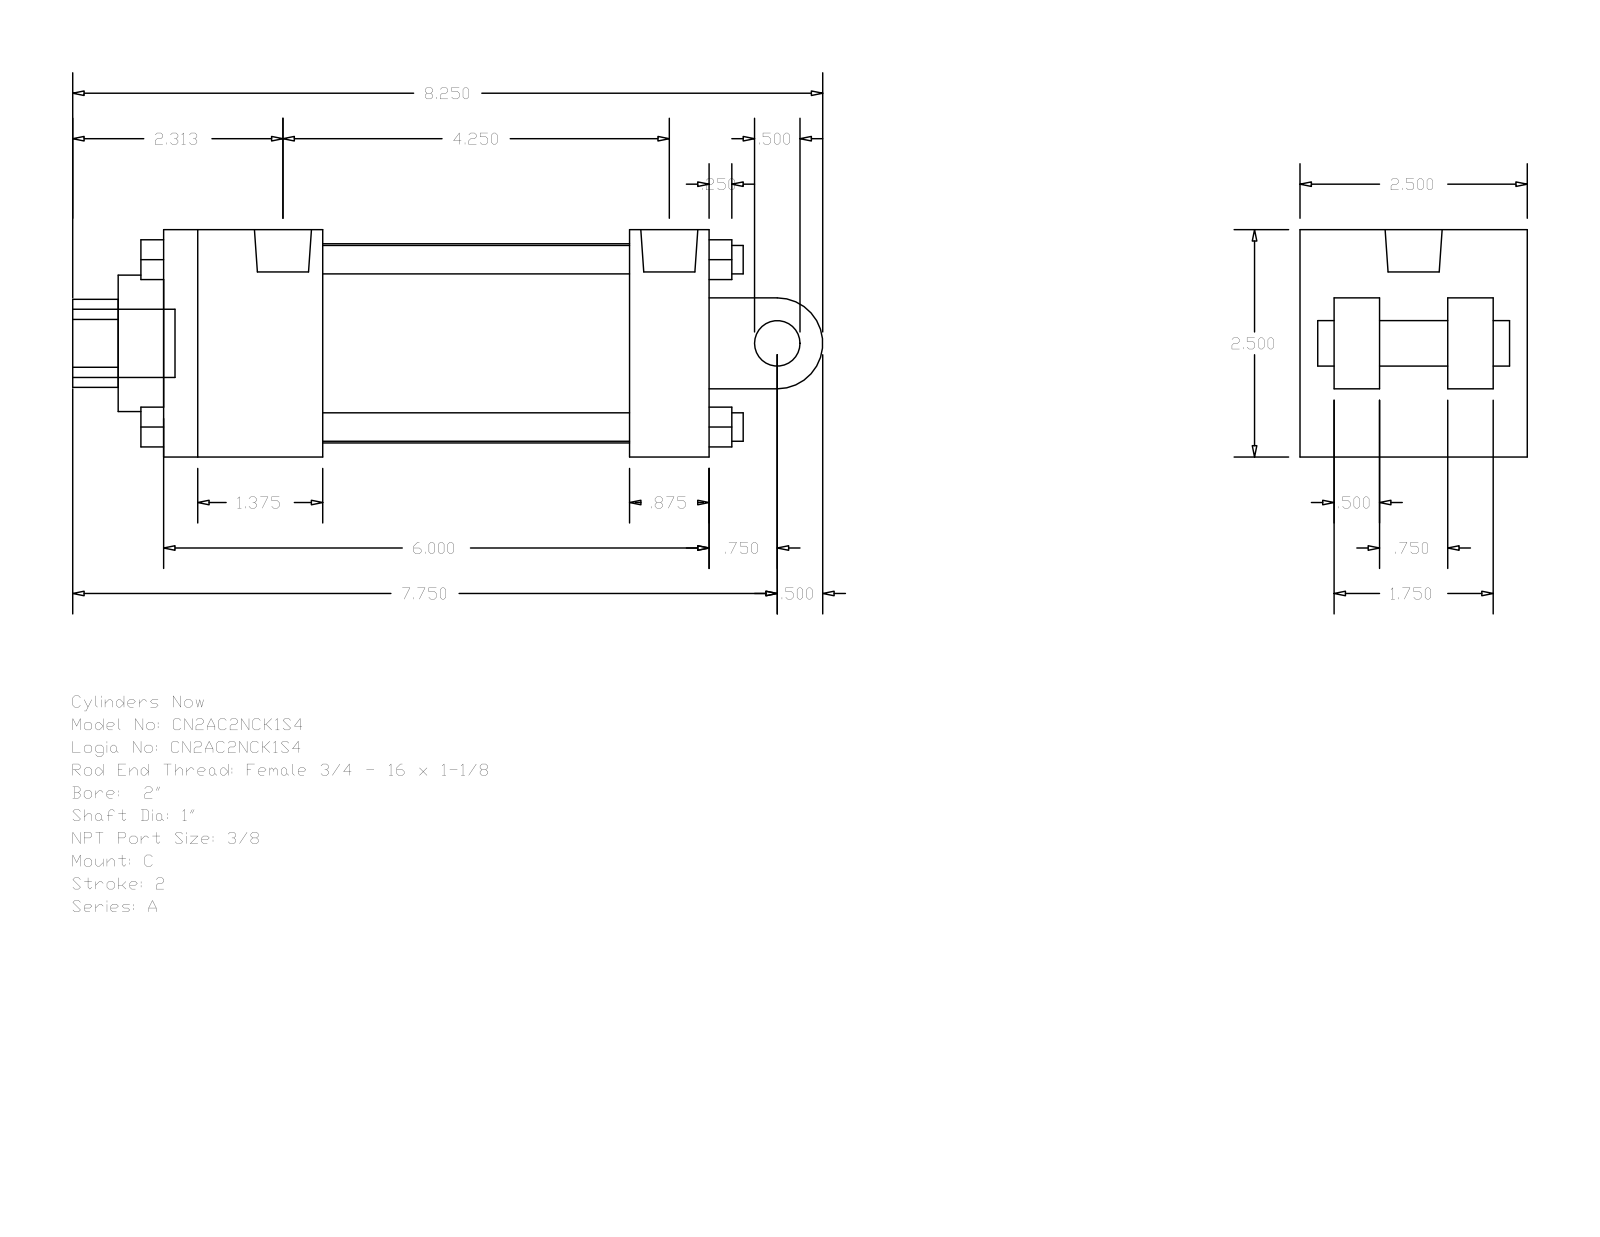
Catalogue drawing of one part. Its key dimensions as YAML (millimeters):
part_name: "A_C__0200_1"
step_written_by: "GSSL Pune (CONFIG_CONTROL_DESIGN)"
units: millimeters
bodies: {solids: 0, faces: 135, planar: 102, cylindrical: 33, other: 0}
overall_size: [209.55, 63.5, 63.5]
round_holes:
  - {diameter: 5.56, count: 2}
  - {diameter: 15.93, count: 1}
  - {diameter: 25.4, count: 1}
  - {diameter: 38.1, count: 1}
  - {diameter: 55.63, count: 1}
round_bosses_or_shafts:
  - {diameter: 7.94, count: 4}
  - {diameter: 5.56, count: 2}
  - {diameter: 19.05, count: 1}
  - {diameter: 15.93, count: 1}
  - {diameter: 12.7, count: 1}
partial_cylinders:
  - {radius: 12.29, count: 1}
  - {radius: 12.7, count: 1}
face_to_face_distances: [63.5, 152.4, 44.45, 12.7, 9.52, 41.28, 107.95, 130.17, 85.72, 22.23]
hole_center_spacings: [3.98]
